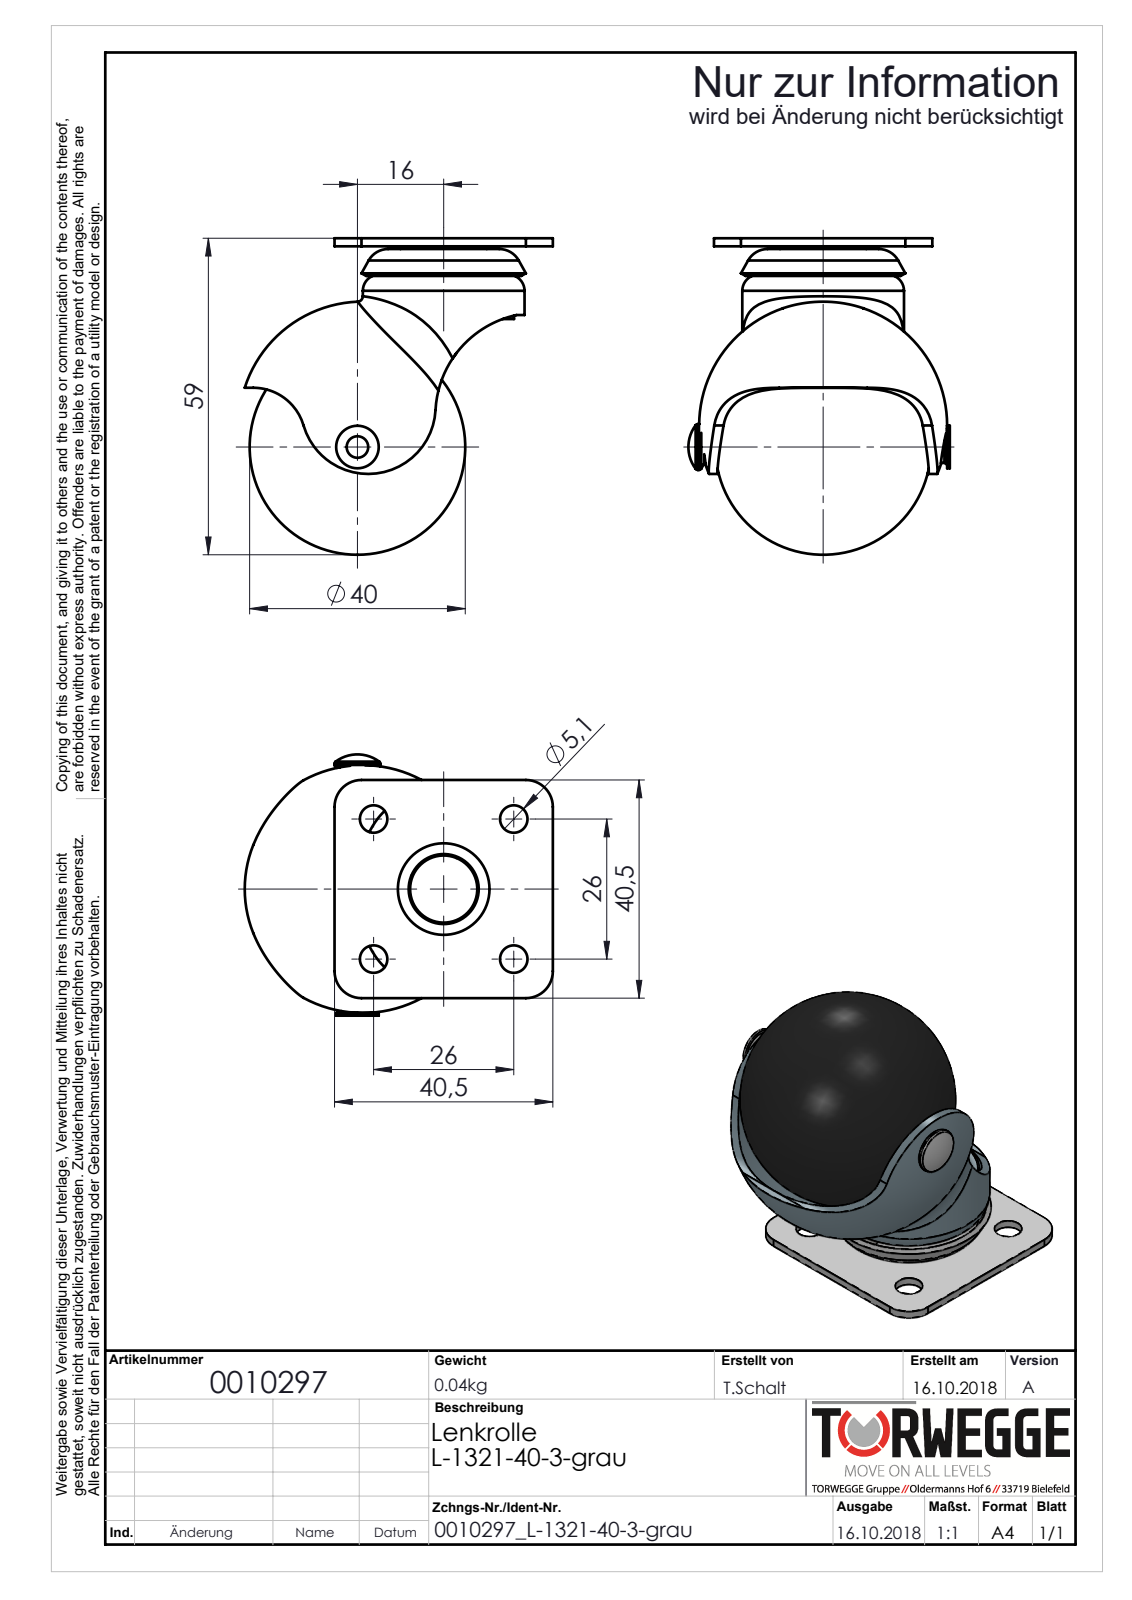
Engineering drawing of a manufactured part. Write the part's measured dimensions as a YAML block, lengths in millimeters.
part_name: "15900rivettato.stp; 165040.stp; 07531.stp; 05706-2.stp (+7 more)"
step_written_by: "SolidWorks 2018 (AUTOMOTIVE_DESIGN)"
units: millimeters
bodies: {solids: 9, faces: 148, planar: 21, cylindrical: 52, other: 75}
overall_size: [58.76, 57.16, 48.5]
volume: 43384
surface_area: 21226
round_holes:
  - {diameter: 5.1, count: 4}
  - {diameter: 4, count: 1}
  - {diameter: 6, count: 1}
  - {diameter: 6.1, count: 1}
  - {diameter: 9, count: 1}
  - {diameter: 9.5, count: 1}
  - {diameter: 11.2, count: 1}
  - {diameter: 27, count: 1}
round_bosses_or_shafts:
  - {diameter: 30, count: 1}
  - {diameter: 26.1, count: 1}
  - {diameter: 11, count: 1}
  - {diameter: 8.9, count: 1}
  - {diameter: 8.5, count: 1}
  - {diameter: 7.9, count: 1}
  - {diameter: 5.9, count: 1}
partial_cylinders:
  - {radius: 5, count: 4}
  - {radius: 9.72, count: 1}
  - {radius: 12.5, count: 1}
  - {radius: 19.04, count: 1}
face_to_face_distances: [1.5, 1, 2.5, 0.5, 3.5, 4, 2, 40.5, 5.5, 7.5]
hole_center_spacings: [18.38, 26, 36.77]
